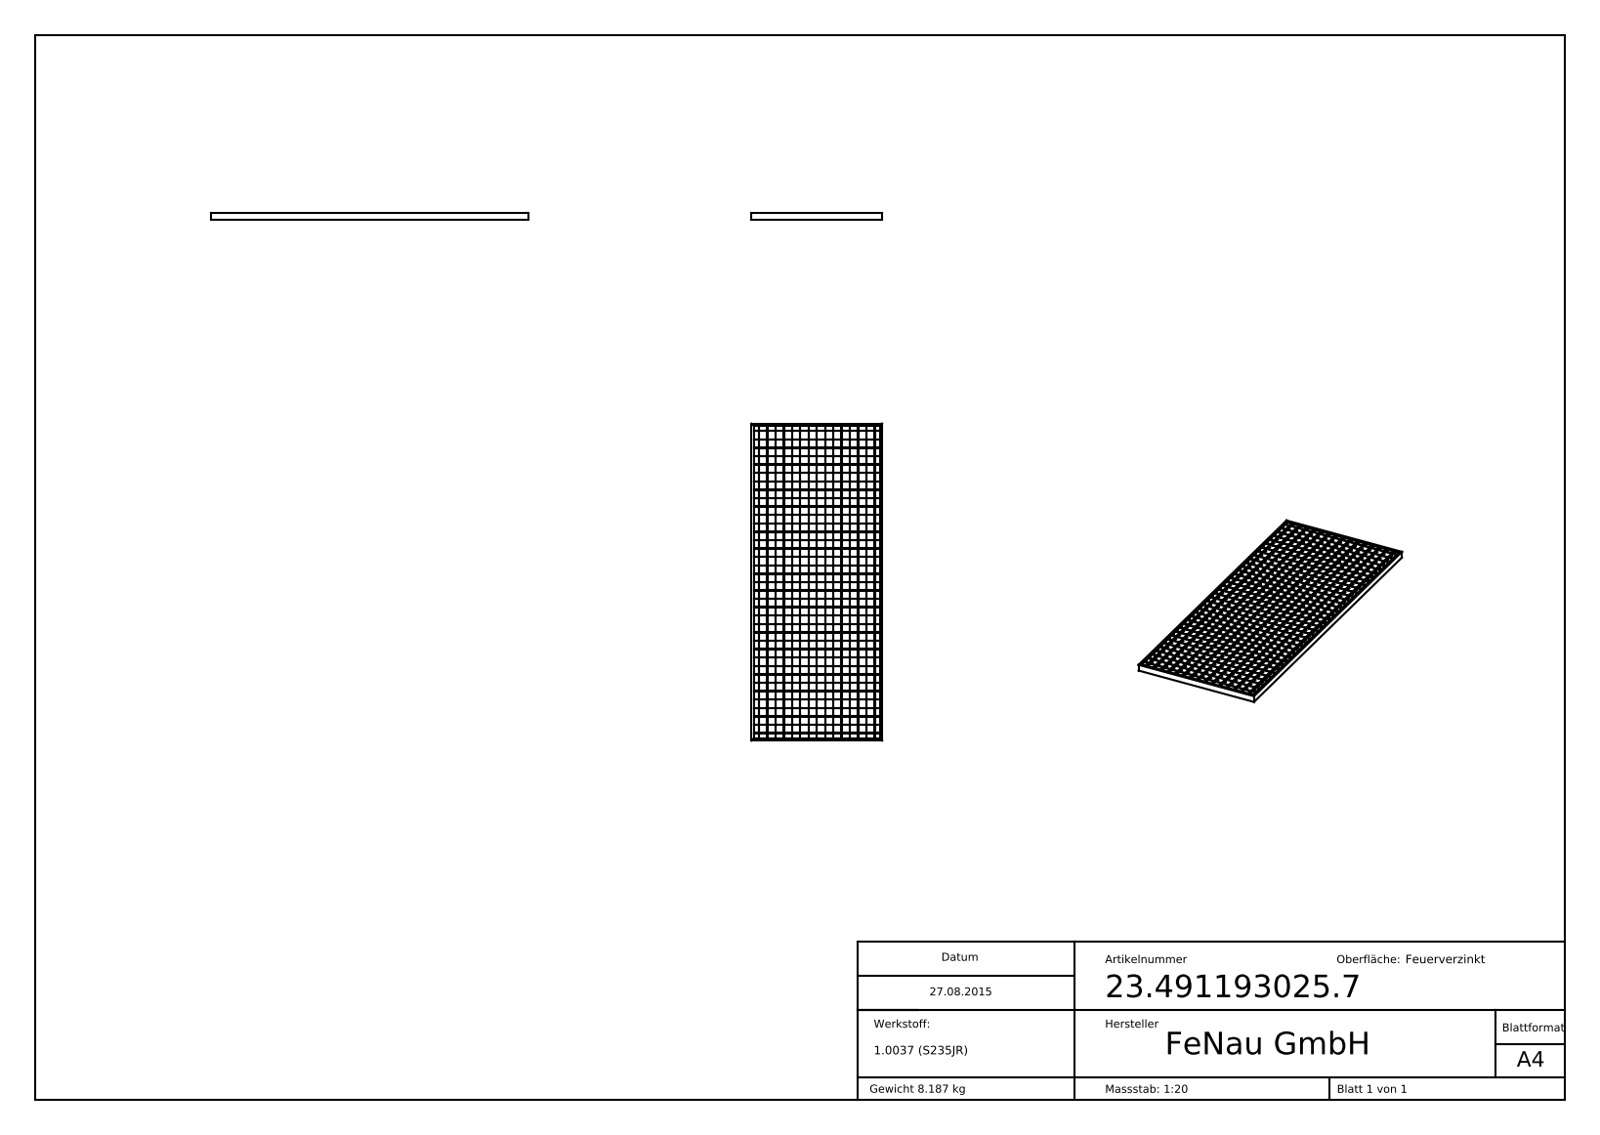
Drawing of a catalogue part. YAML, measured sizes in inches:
part_name: "23-491193025-7"
step_written_by: "SolidWorks 2015 (CONFIG_CONTROL_DESIGN)"
units: inches
bodies: {solids: 1, faces: 2086, planar: 2086, cylindrical: 0, other: 0}
overall_size: [46.85, 19.291, 0.984]
volume: 64.07
surface_area: 2368
face_to_face_distances: [2.48, 1.24, 3.72, 4.961, 6.201, 1.22, 7.441, 8.681, 9.921, 2.441]
